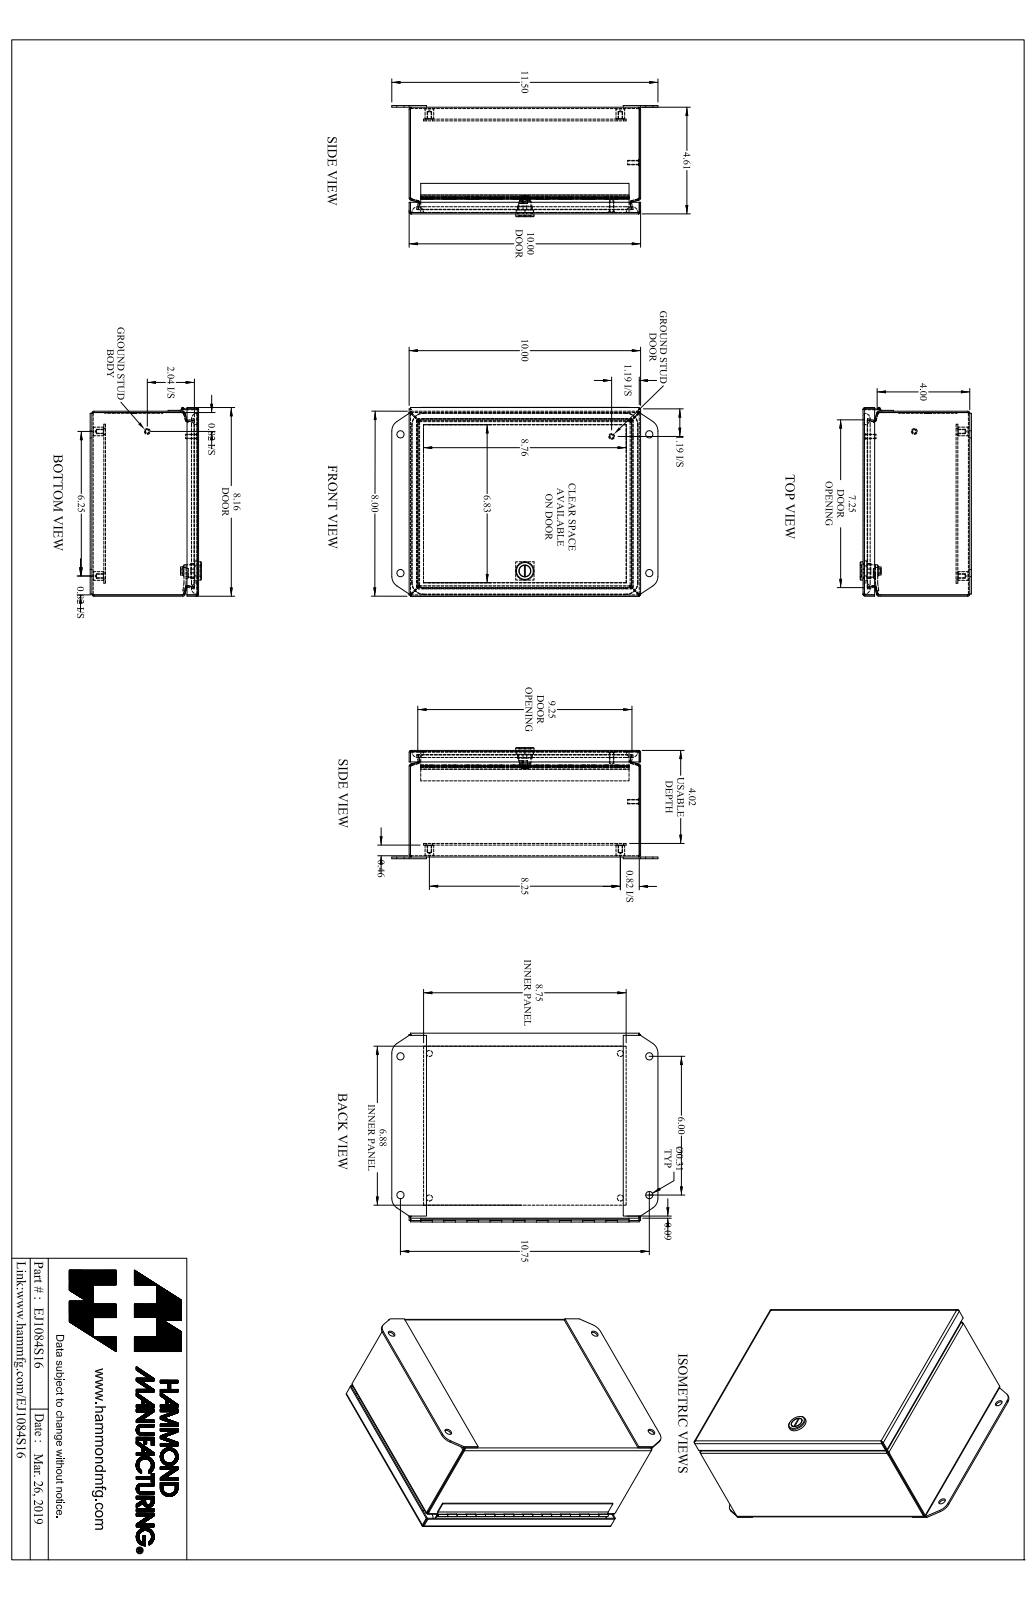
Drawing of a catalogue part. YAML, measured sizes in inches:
part_name: "EJ1084S16_Default"
step_written_by: "SolidWorks 2019 (CONFIG_CONTROL_DESIGN)"
units: inches
bodies: {solids: 16, faces: 596, planar: 310, cylindrical: 206, other: 80}
overall_size: [11.5, 8.165, 4.805]
volume: 29.38
surface_area: 966.3
round_holes:
  - {diameter: 0.156, count: 4}
  - {diameter: 0.265, count: 4}
  - {diameter: 0.313, count: 4}
  - {diameter: 0.05, count: 1}
  - {diameter: 0.516, count: 1}
round_bosses_or_shafts:
  - {diameter: 0.375, count: 4}
  - {diameter: 0.25, count: 2}
  - {diameter: 0.19, count: 2}
  - {diameter: 0.788, count: 1}
  - {diameter: 0.535, count: 1}
  - {diameter: 0.496, count: 1}
  - {diameter: 0.435, count: 1}
  - {diameter: 0.1, count: 1}
partial_cylinders:
  - {radius: 0.029, count: 16}
  - {radius: 0.086, count: 16}
  - {radius: 0.281, count: 12}
  - {radius: 0.25, count: 4}
  - {radius: 0.499, count: 4}
  - {radius: 0.5, count: 4}
  - {radius: 0.06, count: 2}
  - {radius: 0.03, count: 1}
face_to_face_distances: [0.057, 4.554, 0.072, 0.589, 4.611, 4.497, 7.943, 9.943, 4.094, 4.037]
hole_center_spacings: [1.257, 9.501, 8.25, 4.131, 6.252, 10.35, 11.304, 5.376]
